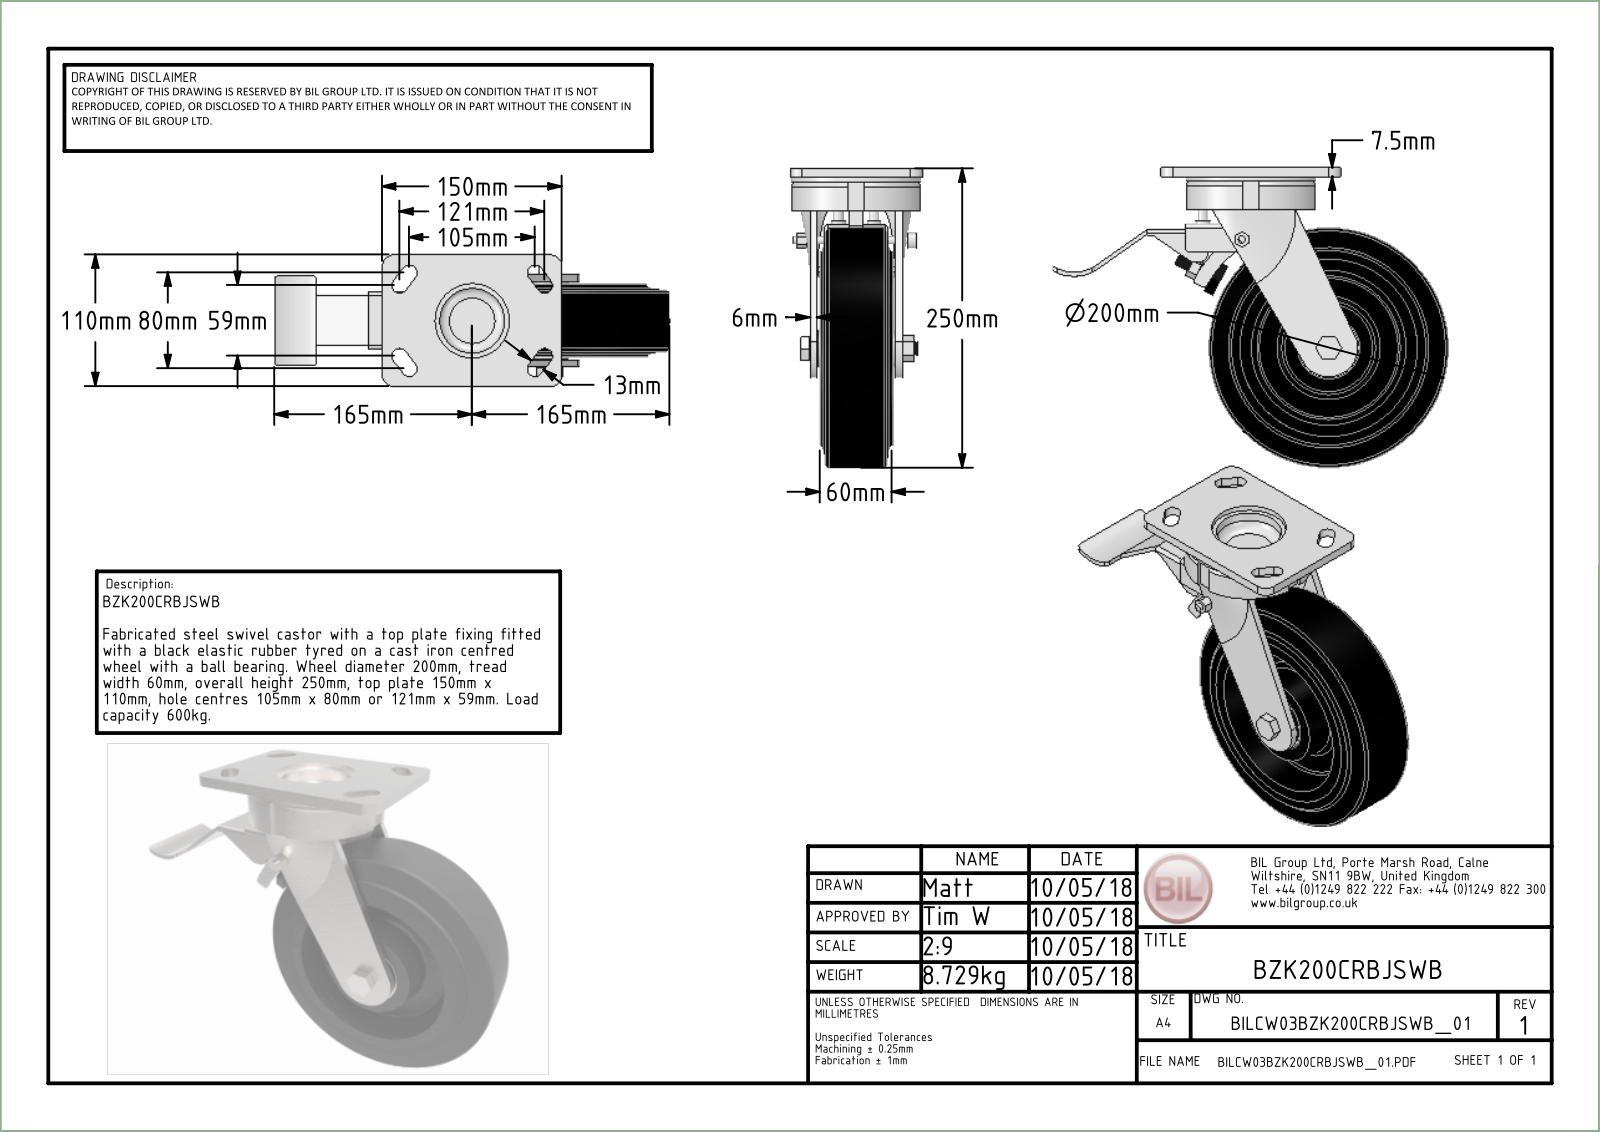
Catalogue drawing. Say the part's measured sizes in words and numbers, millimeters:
The part is named "BZK200CRBJSWB v3; BZK200ASSWB v1; FABRICATED STEEL TOP PLATE; FABRICATED STEEL FORKS (+8 more)". Its 3-D file was written by "Autodesk Translation Framework v13.14.0.145 (AUTOMOTIVE_DESIGN)". It is 58 solids with 1258 faces: 523 planar, 367 cylindrical and 368 other. Overall it measures 310 by 250 by 115.22 millimeters. Its volume is 1 782 000 cubic millimeters and its surface area 411 856 square millimeters. Round holes: 5 of diameter 6, 2 of diameter 10, 1 of diameter 5, 1 of diameter 8, 1 of diameter 12, 1 of diameter 12.5, 1 of diameter 13, 1 of diameter 14, 1 of diameter 25, 1 of diameter 34.35, 1 of diameter 35.85, 1 of diameter 36. Round bosses or shafts: 3 of diameter 12, 2 of diameter 8, 1 of diameter 163, 1 of diameter 108, 1 of diameter 107, 1 of diameter 45.71, 1 of diameter 44.32, 1 of diameter 36.85. Partial cylindrical surfaces (rounded edges, fillets, slot ends): 50 of radius 0.5, 11 of radius 1, 8 of radius 6, 8 of radius 6.75, 5 of radius 2.5, 5 of radius 10, 4 of radius 0.47, 4 of radius 0.9. The main face-to-face distances are 24, 9, 36, 3, 6, 12, 71, 7.5, 8, 62. The hole center spacings are 50.23, 14.12, 15.62, 26.42, 36.19, 38, 39.54, 42.39.
